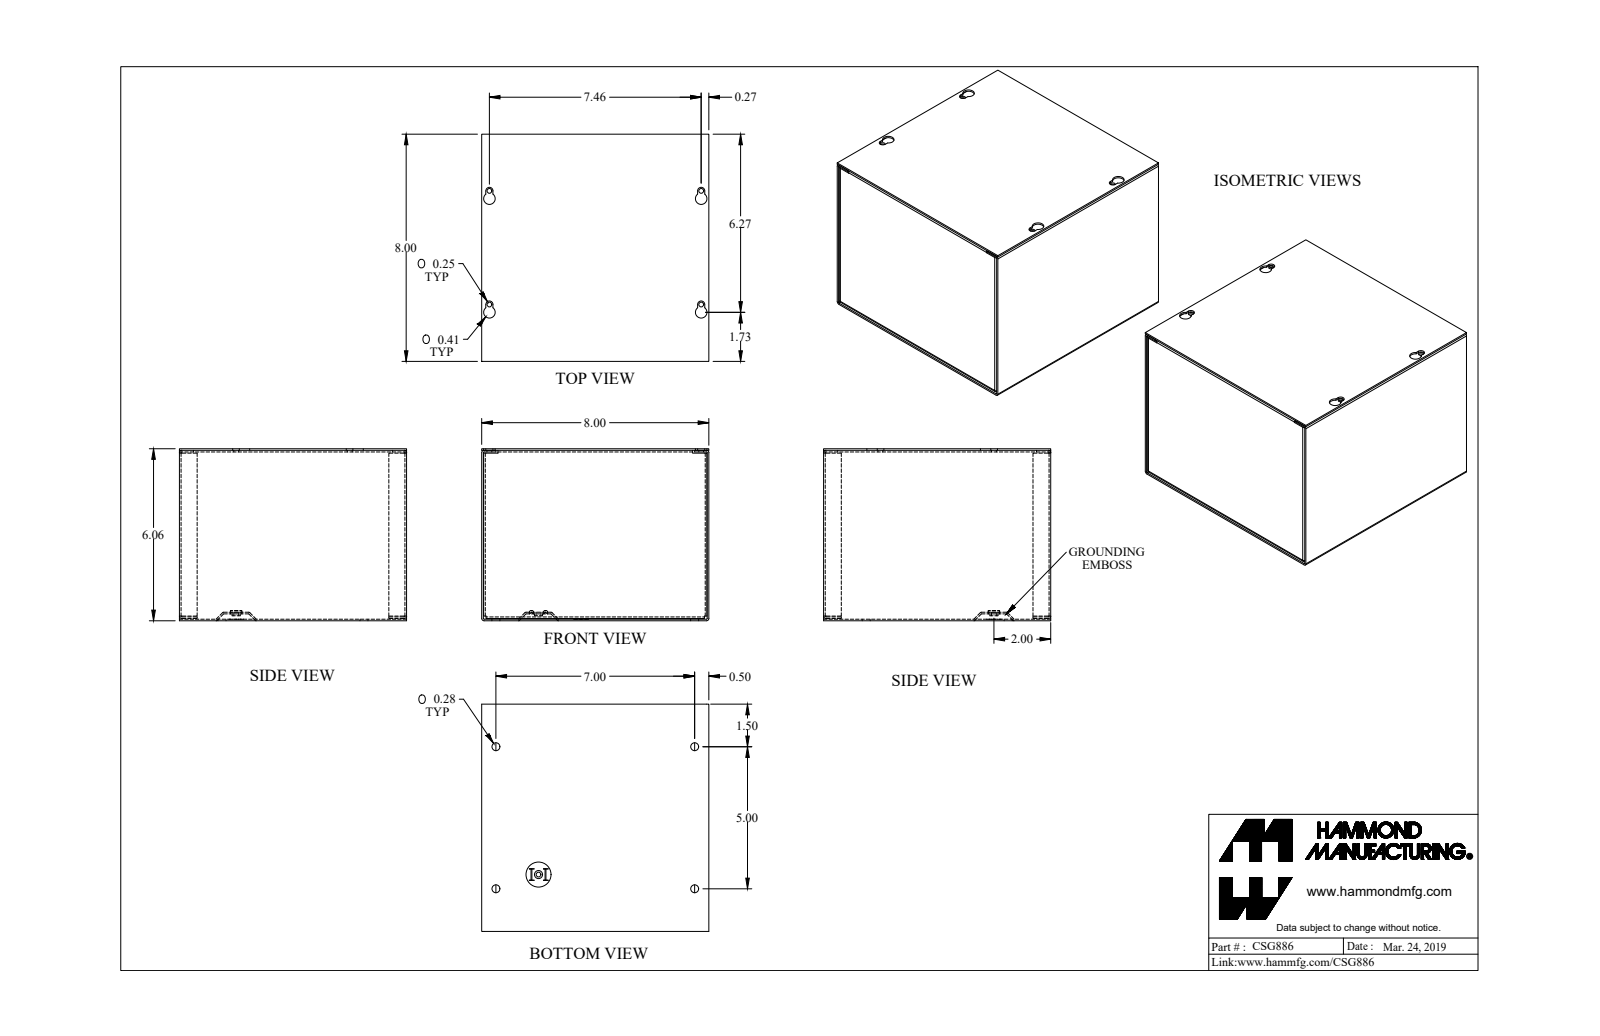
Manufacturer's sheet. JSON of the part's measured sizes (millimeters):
{"part_name": "CSG886_Default", "step_written_by": "SolidWorks 2019 (CONFIG_CONTROL_DESIGN)", "units": "millimeters", "bodies": {"solids": 4, "faces": 205, "planar": 125, "cylindrical": 72, "other": 8}, "overall_size": [203.2, 203.2, 153.8], "volume_mm3": 325300, "surface_area_mm2": 455400, "round_holes": [[4.3, 5], [7.1, 4], [12.7, 1]], "round_bosses_or_shafts": [[12.5, 1], [7.2, 1]], "partial_cylinders_radius": [[0.7, 12], [2.2, 12], [1.4, 8], [3.2, 4], [5.2, 4]], "face_to_face_distances": [1.4, 201.8, 152.4, 203.2, 200.3, 151, 153.8, 1.8, 200, 2], "hole_center_spacings": [14, 114.5, 184.1, 216.3, 101.6, 127, 177.8, 189.5]}
